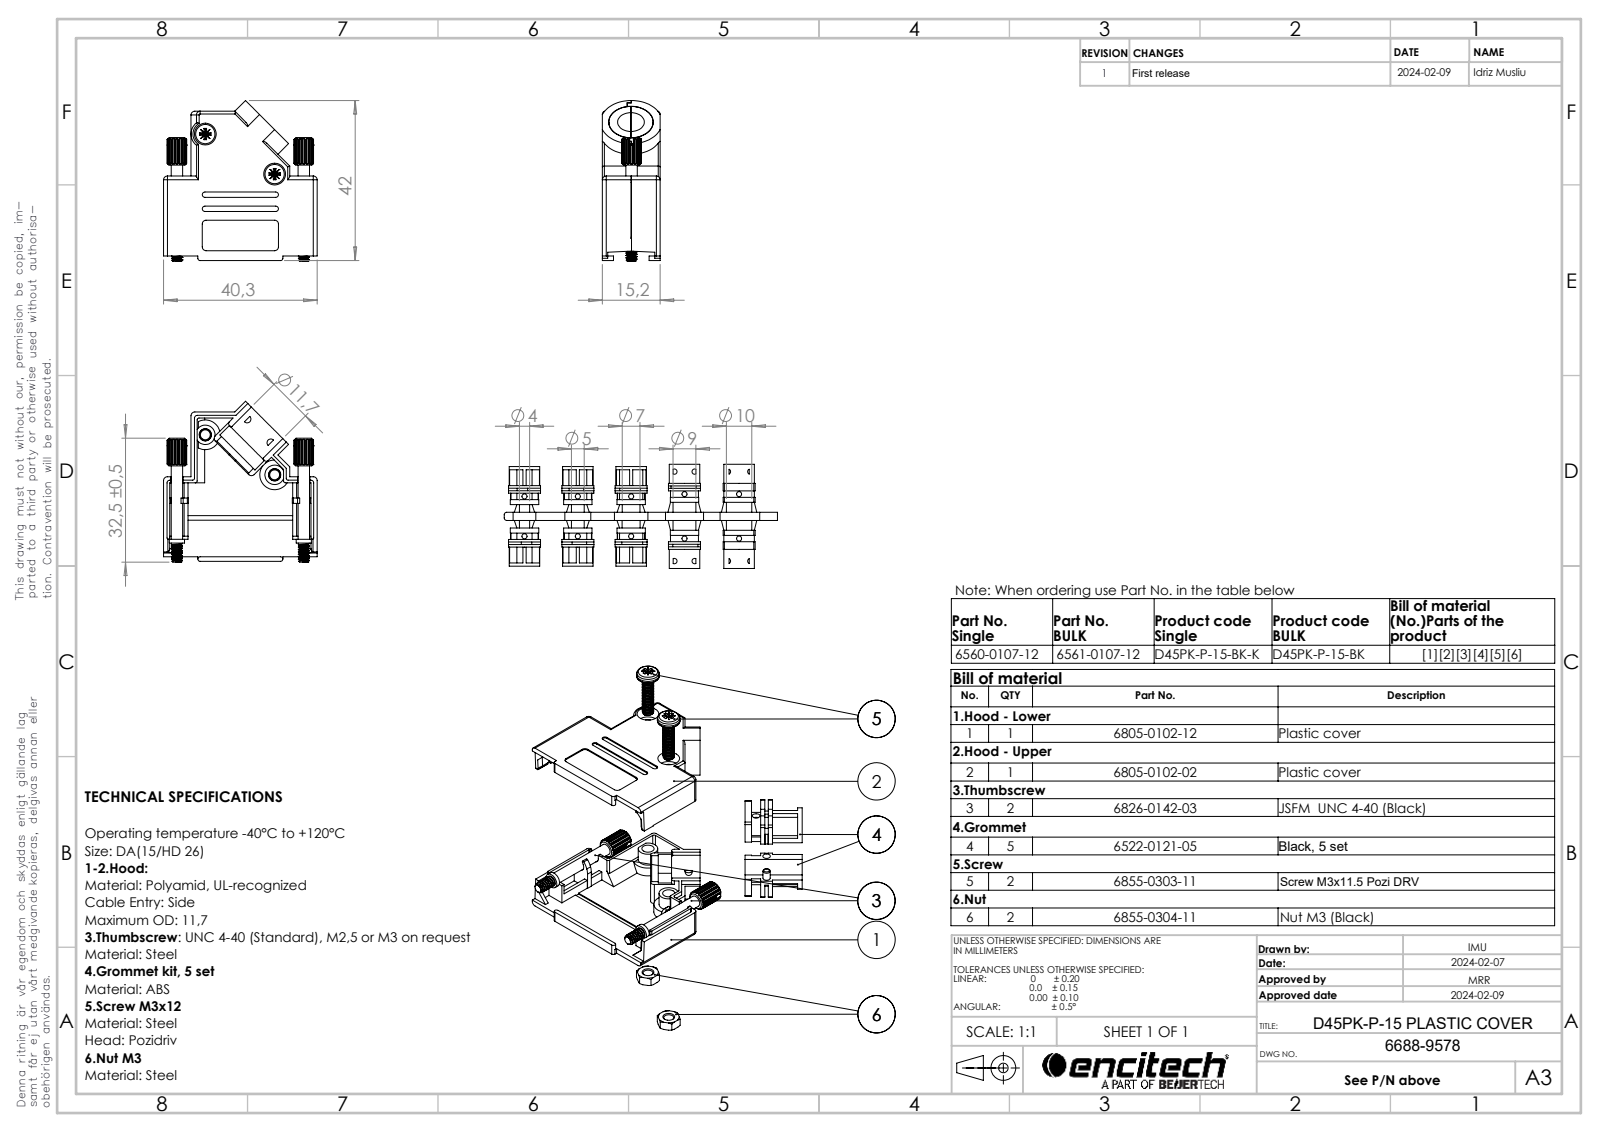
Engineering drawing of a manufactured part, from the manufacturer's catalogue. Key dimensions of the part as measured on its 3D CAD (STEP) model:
Part name (STEP PRODUCT): 6688-9578; 6855-0303-01; 6805-0146-12; 6522-0121-05 (7mm) (+3 more)
STEP written by: SolidWorks 2021 (AUTOMOTIVE_DESIGN)
Units: millimetres
Bodies: 10 solids, 925 faces (548 planar, 265 cylindrical, 112 other)
Overall size (bounding box): 42.2 × 40.3 × 15.15
Volume: 7 984 mm³ · Surface area: 12 771 mm²
Round holes (diameter × count): ⌀2 ×3, ⌀2.6 ×2, ⌀3.2 ×2, ⌀5.7 ×2, ⌀7 ×1, ⌀11.7 ×1
Round bosses / shafts (diameter × count): ⌀5.1 ×2, ⌀4 ×2, ⌀3 ×2, ⌀2.9 ×2, ⌀2.8 ×2, ⌀1.9 ×2, ⌀11.6 ×1, ⌀9.2 ×1
Partial cylindrical surfaces — rounded edges, fillets, slot ends (radius × count): R0.5 ×23, R1 ×19, R0.75 ×13, R0.1 ×8, R0.7 ×4, R1.6 ×4, R5.91 ×4, R0.33 ×2
Main face-to-face distances: 1.4, 13.75, 1.6, 15.15, 12.35, 7.2, 1.1, 7.5, 14.85, 13.45
Hole centre spacings: 5.71, 6.06, 6.16, 9.37, 10, 11.71, 14.88, 16.1
